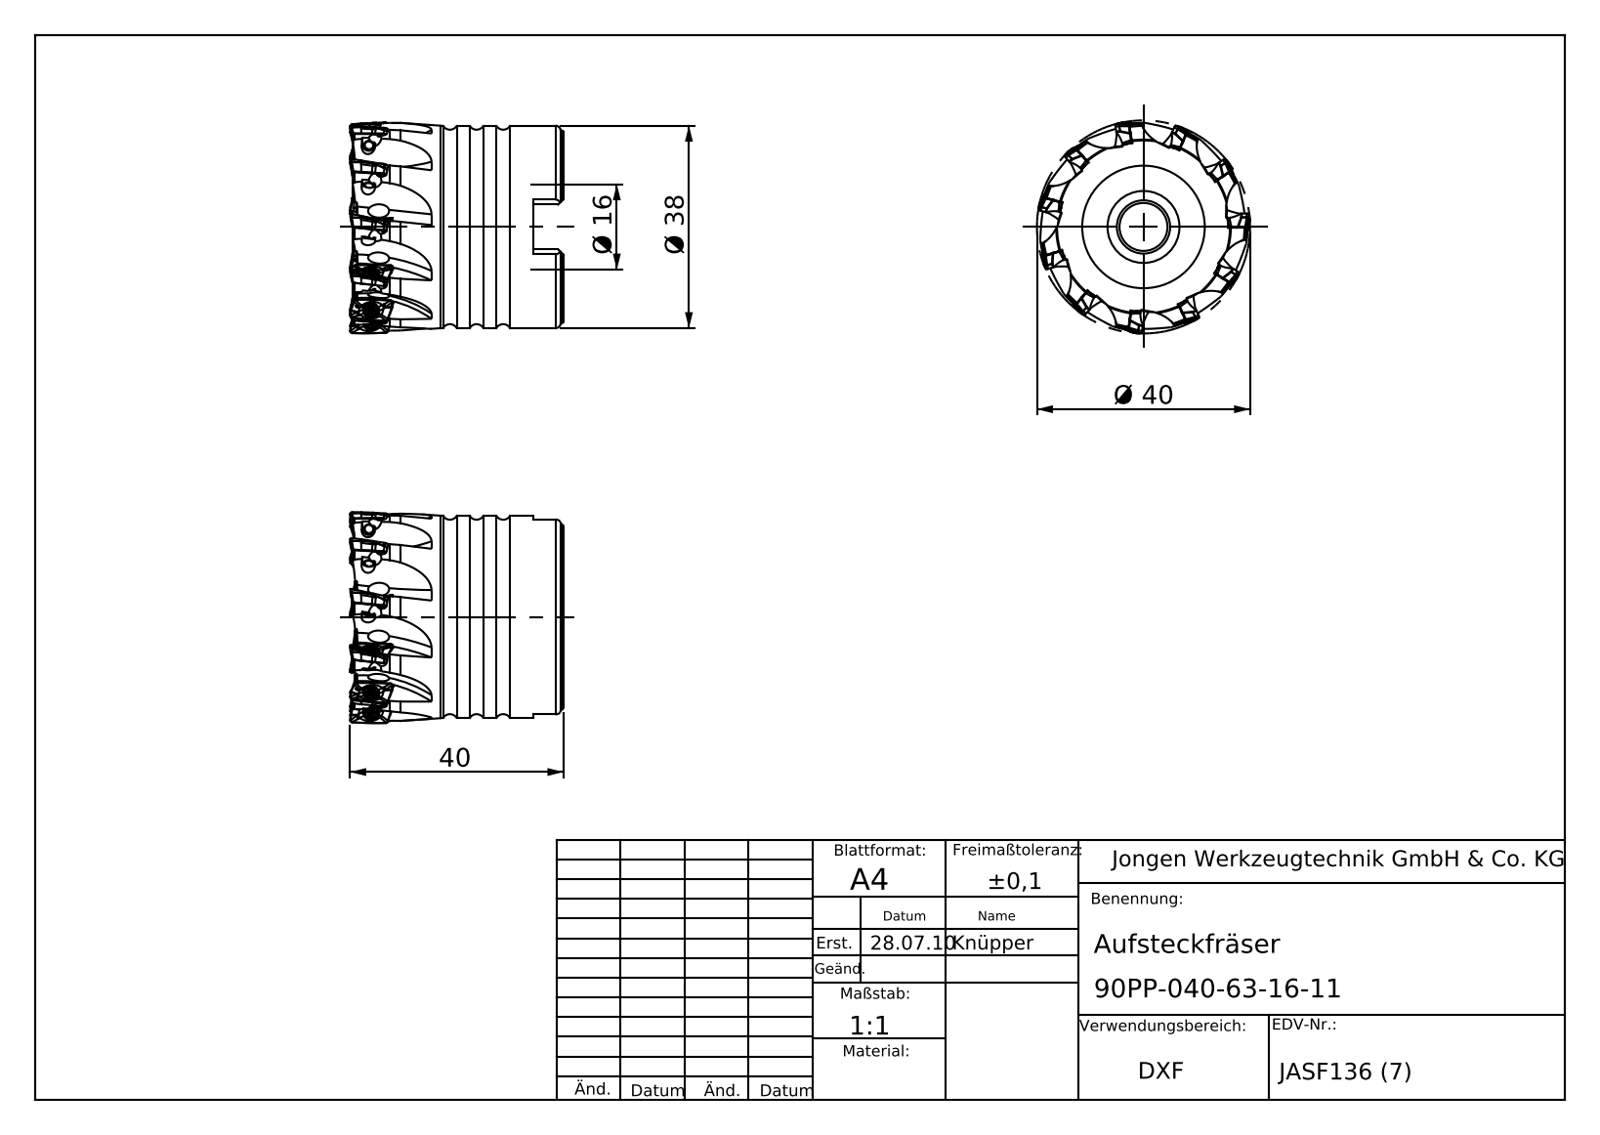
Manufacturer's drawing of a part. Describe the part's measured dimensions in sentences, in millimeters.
The part is named "90PP-040-63-16-11". Its 3-D file was written by "SolidWorks 2011 (AUTOMOTIVE_DESIGN)". It is 1 solid with 247 faces: 85 planar, 63 cylindrical and 99 other. Overall it measures 40 by 40 by 40 millimeters. Its volume is 35 009 cubic millimeters and its surface area 11 553 square millimeters. Round holes: 11 of diameter 2.5, 1 of diameter 9, 1 of diameter 13.5, 1 of diameter 16, 1 of diameter 16.15, 1 of diameter 16.3. Round bosses or shafts: 1 of diameter 38. Partial cylindrical surfaces (rounded edges, fillets, slot ends): 11 of radius 20, 1 of radius 19.53. The main face-to-face distances are 38.15, 5.6, 32.55, 39.5, 33.9, 1.35, 8.4, 27.15, 21.55, 11.
